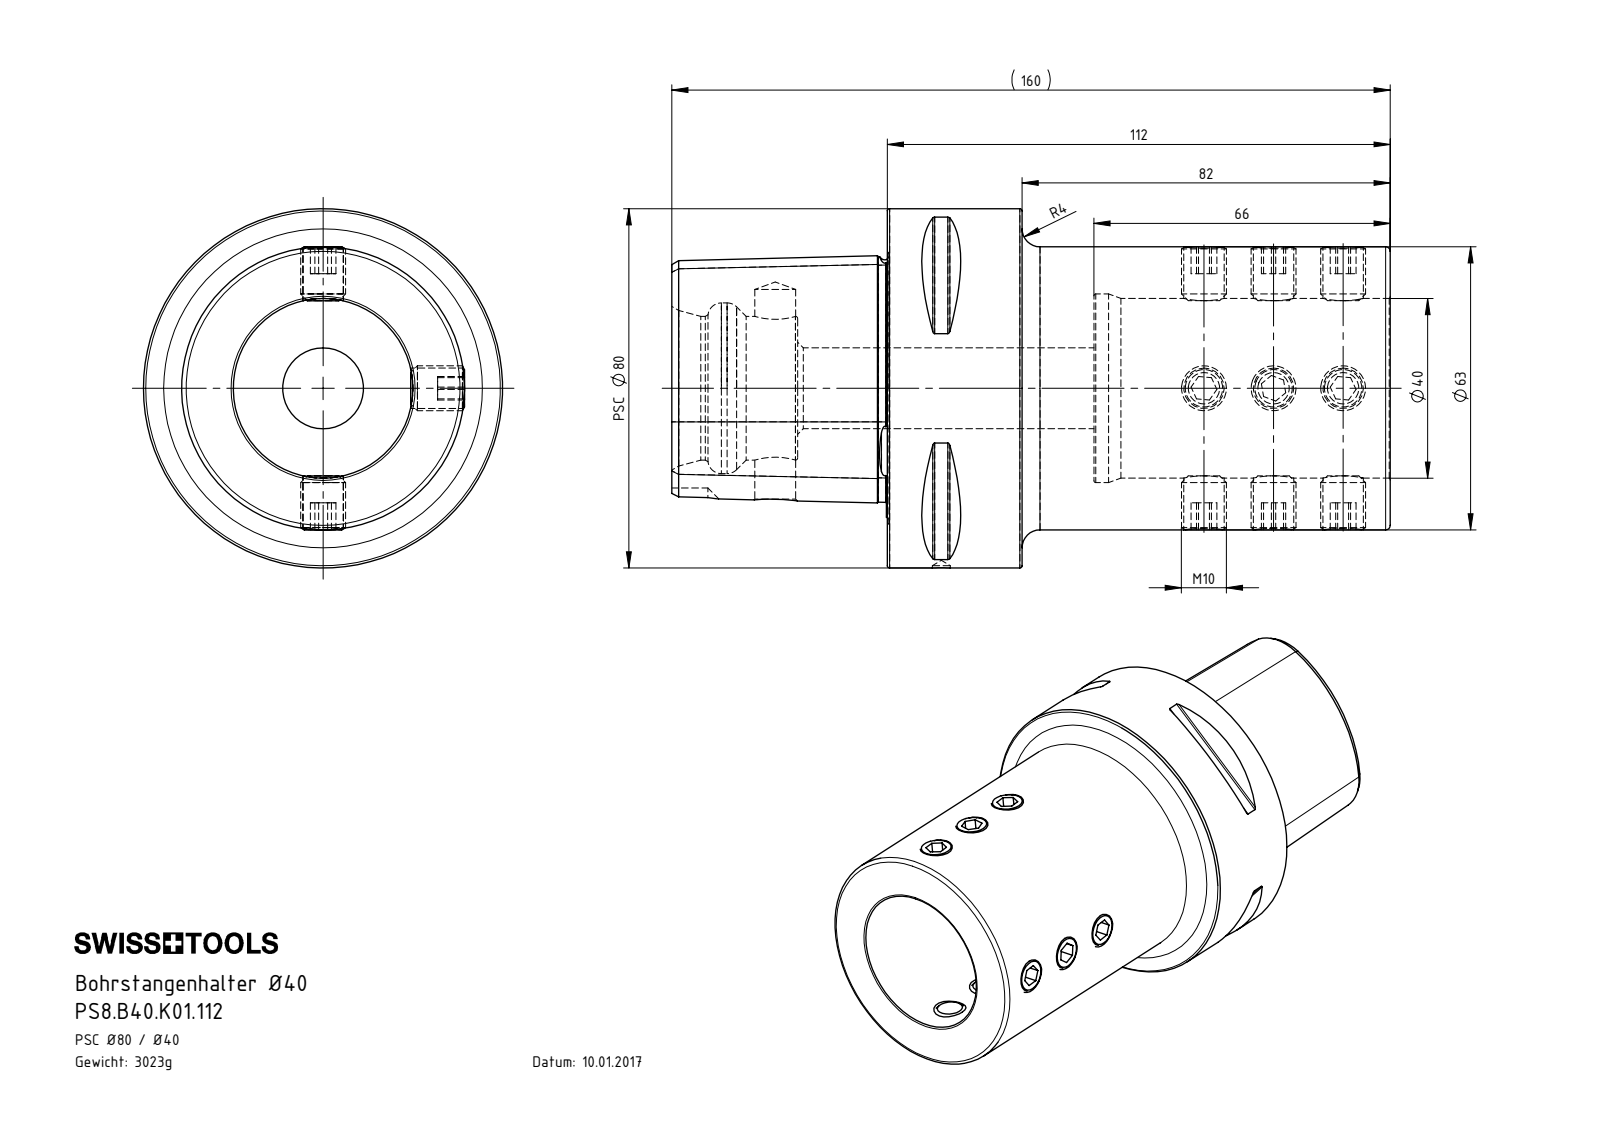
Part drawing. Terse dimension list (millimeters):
name: ISO 4026 - M10 x 12_PreviewCfg; PS8.B40.K01.112; PS8-B40.K01.112_A
written by: SolidWorks 2015 (AUTOMOTIVE_DESIGN)
unit: mm
bodies: 10 solids, 292 faces (102 planar, 67 cylindrical, 123 other)
size: 160 × 80 × 80
volume: 385 142 mm³; area: 63 832 mm²
holes: 6× ⌀9, 1× ⌀4, 1× ⌀9.1, 1× ⌀18, 1× ⌀32, 1× ⌀38, 1× ⌀40, 1× ⌀42
bosses: 6× ⌀10, 1× ⌀80, 1× ⌀63
rounds: 8× R0.5, 1× R6
face distances: 112, 66, 46, 48, 94, 160, 78, 30, 16, 82
hole spacings: 15.5, 31, 37, 58.5, 74, 89.5, 95.5, 111
